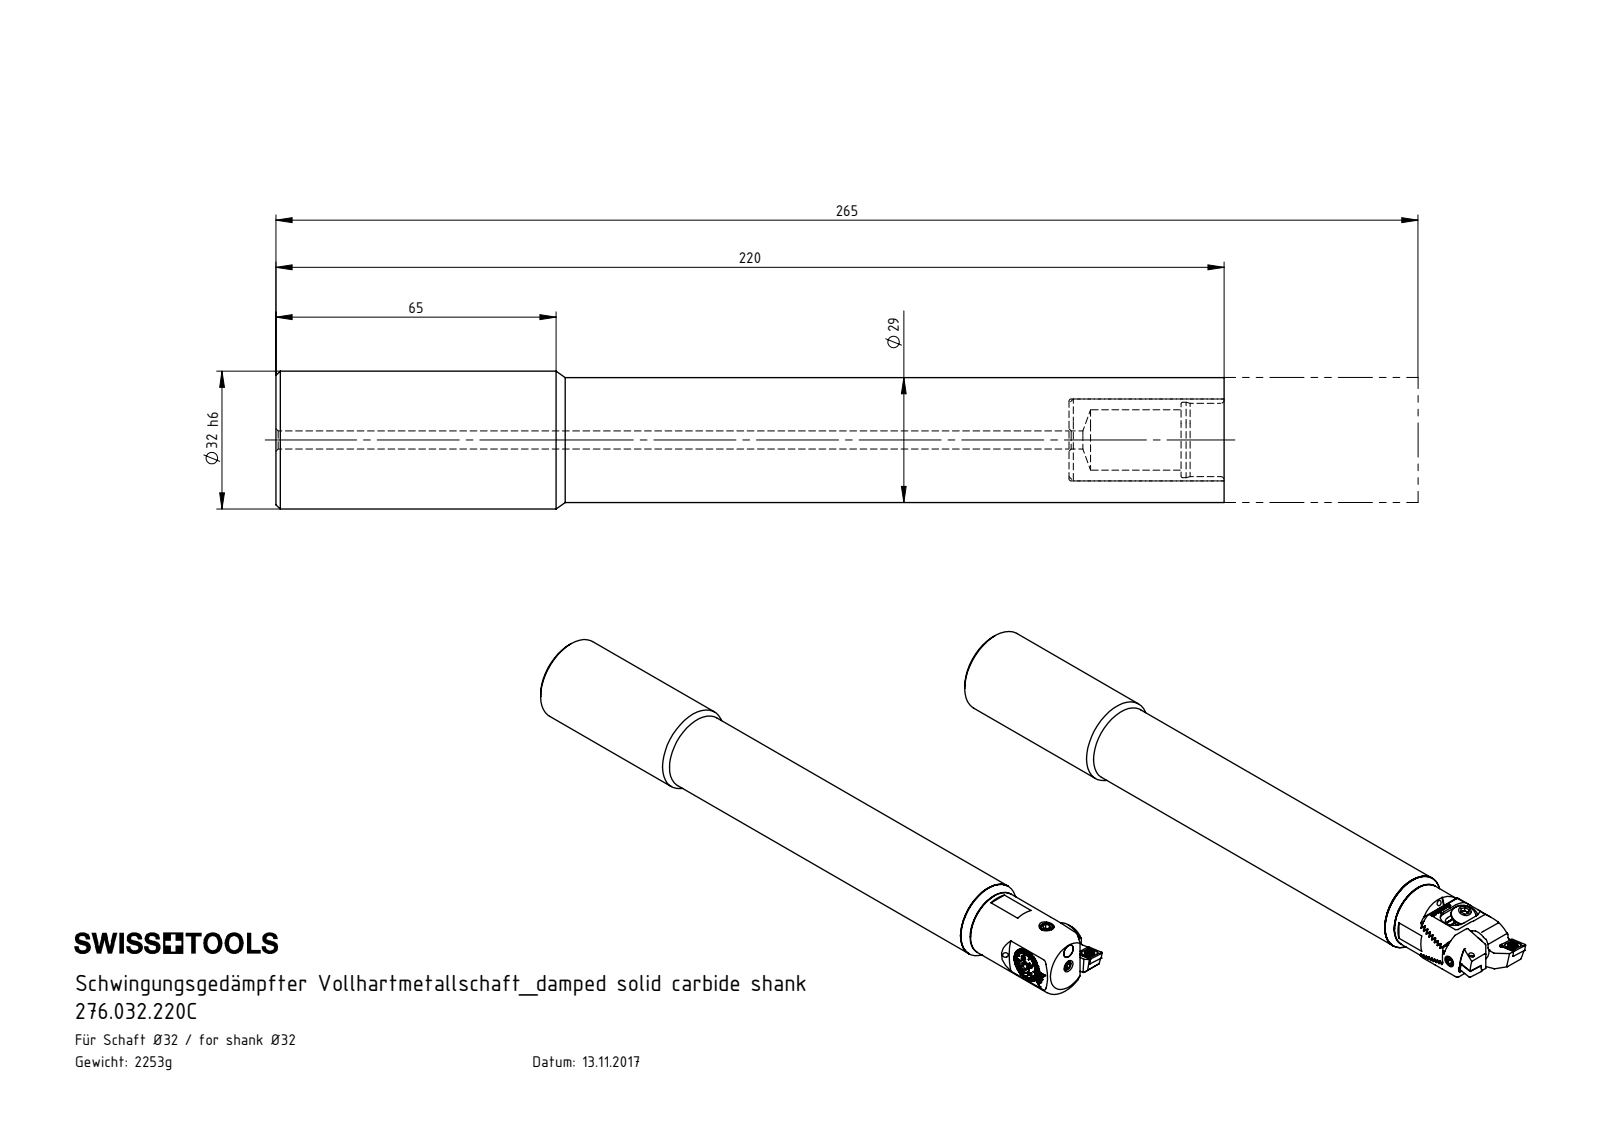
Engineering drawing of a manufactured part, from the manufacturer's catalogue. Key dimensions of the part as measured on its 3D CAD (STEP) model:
Part name (STEP PRODUCT): 276.032.220C; HP5-ER1.019.036_A; HP5-Z25.030.045_fr D29-Schaft; D29-D25.HP5.003_A (+8 more)
STEP written by: SolidWorks 2017 (CONFIG_CONTROL_DESIGN)
Units: millimetres
Bodies: 19 solids, 1088 faces (510 planar, 274 cylindrical, 304 other)
Overall size (bounding box): 265 × 32 × 32
Volume: 167 210 mm³ · Surface area: 45 730 mm²
Round holes (diameter × count): ⌀2 ×6, ⌀4.2 ×3, ⌀1.6 ×2, ⌀2.05 ×2, ⌀2.8 ×2, ⌀3.85 ×2, ⌀6 ×2, ⌀2.5 ×1, ⌀3.3 ×1, ⌀3.5 ×1, ⌀5.3 ×1, ⌀10.6 ×1
Round bosses / shafts (diameter × count): ⌀9.5 ×2, ⌀5 ×2, ⌀4 ×2, ⌀3.4 ×2, ⌀2.5 ×2, ⌀32 ×1, ⌀29 ×1, ⌀25 ×1
Partial cylindrical surfaces — rounded edges, fillets, slot ends (radius × count): R0.12 ×18, R0.5 ×18, R0.12 ×16, R0.21 ×12, R0.36 ×10, R2 ×4, R2.8 ×4, R5 ×4
Main face-to-face distances: 1.43, 3, 220, 223, 2.86, 39, 184, 36, 1.39, 10
Hole centre spacings: 3.91, 4.01, 7, 19.06, 19.15, 21.97, 13.52, 15.9
